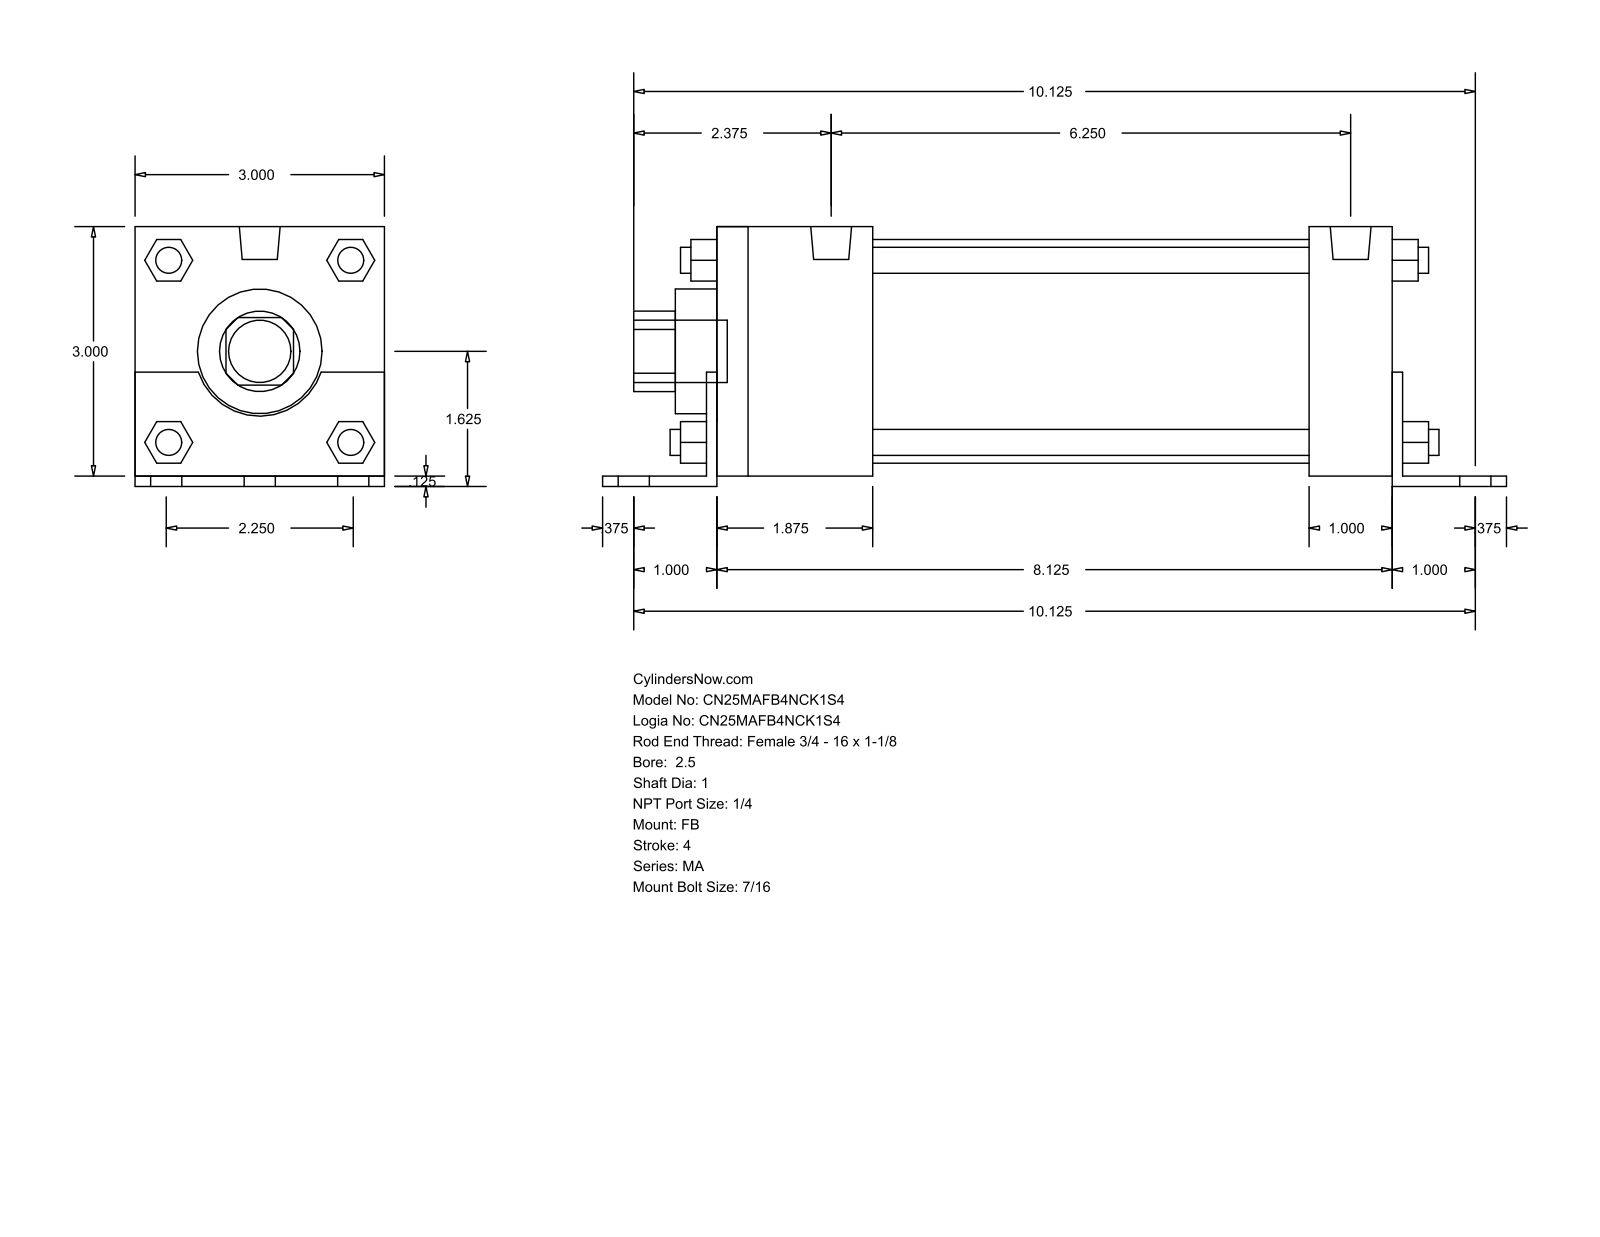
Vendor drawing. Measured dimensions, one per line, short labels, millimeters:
name: MA_FB__0250_1
written by: GSSL Pune (CONFIG_CONTROL_DESIGN)
unit: mm
bodies: 0 solids, 140 faces (105 planar, 35 cylindrical, 0 other)
size: 276.23 × 79.38 × 76.2
holes: 1× ⌀25.4, 1× ⌀38.1, 1× ⌀68.33
bosses: 8× ⌀7.94, 6× ⌀11.11, 2× ⌀12.49, 1× ⌀19.05
rounds: 1× R12.29, 1× R19.81
face distances: 76.2, 3.17, 79.37, 209.55, 206.38, 12.7, 25.4, 28.57, 47.63, 158.75
